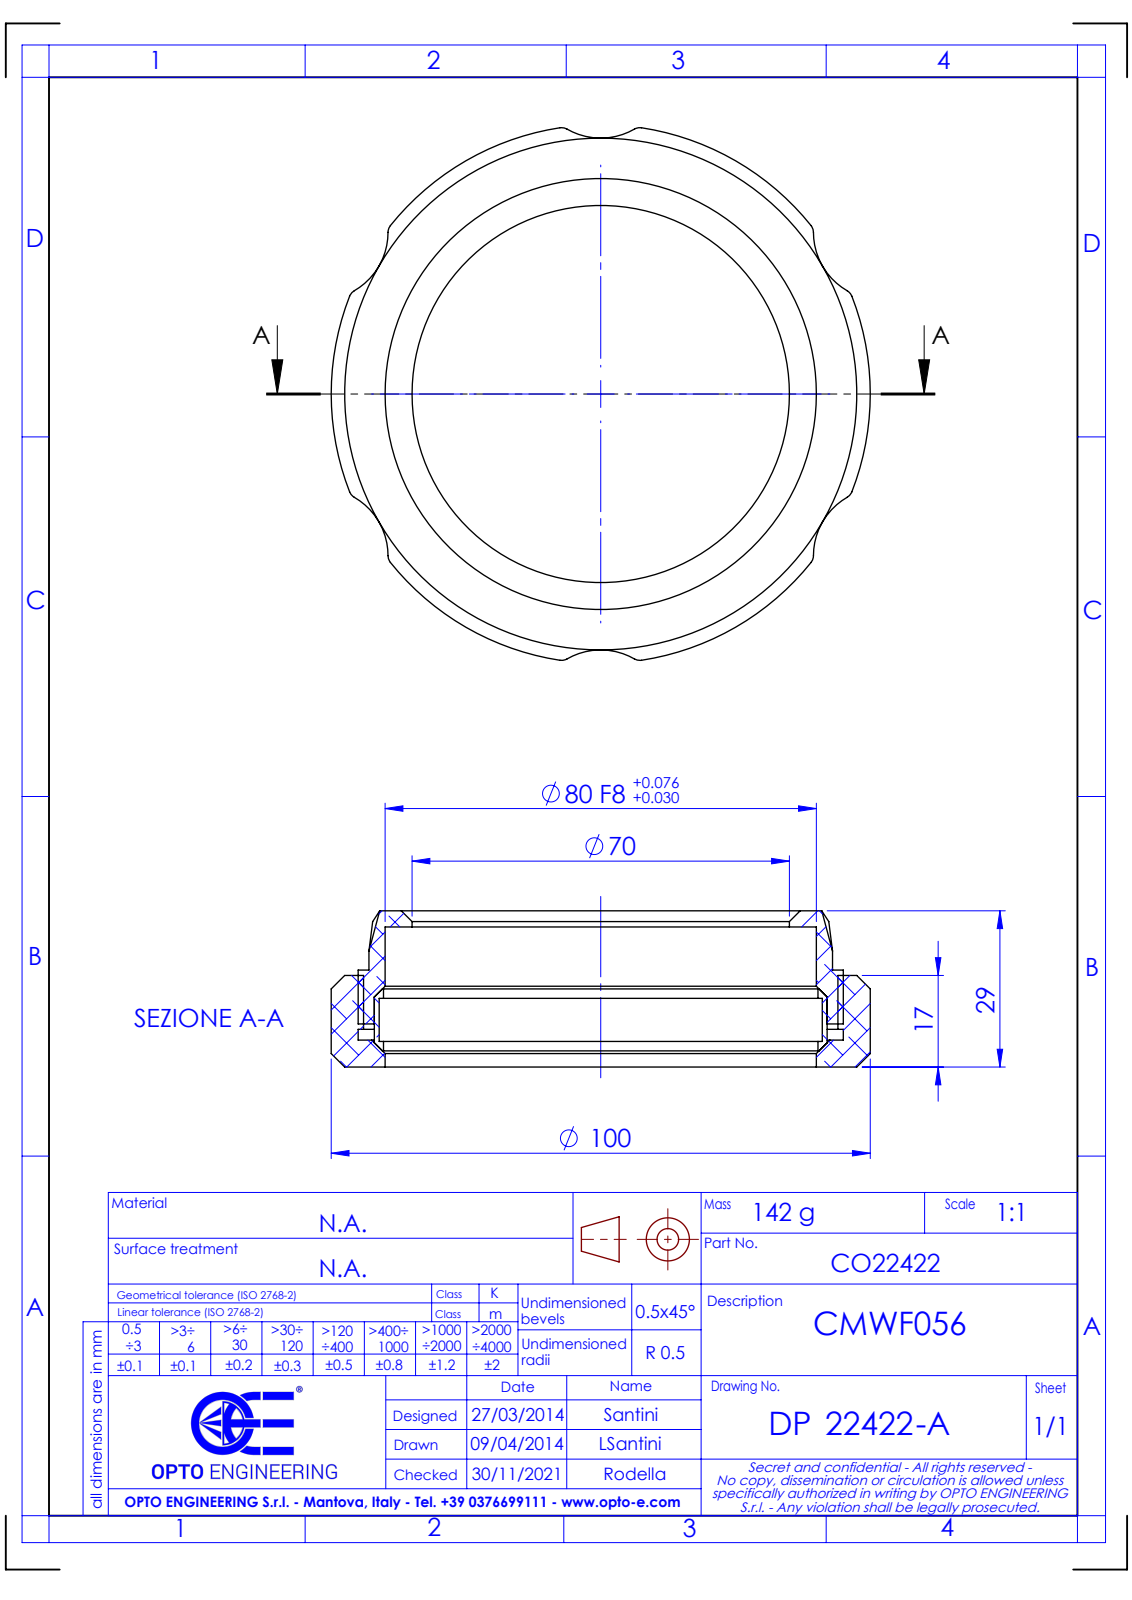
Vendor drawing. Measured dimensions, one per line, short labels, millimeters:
name: DP22422 -A_CMWF056
written by: SolidWorks 2021 (CONFIG_CONTROL_DESIGN)
unit: mm
bodies: 0 solids, 103 faces (14 planar, 63 cylindrical, 26 other)
size: 100 × 98.9 × 29
holes: 1× ⌀70, 1× ⌀80, 1× ⌀80.6, 1× ⌀82.2, 1× ⌀84, 1× ⌀88
bosses: 1× ⌀90, 1× ⌀86
rounds: 12× R2, 6× R12.5, 6× R40, 1× R50
face distances: 9, 3, 12, 8, 21, 18, 26, 17, 29, 1
